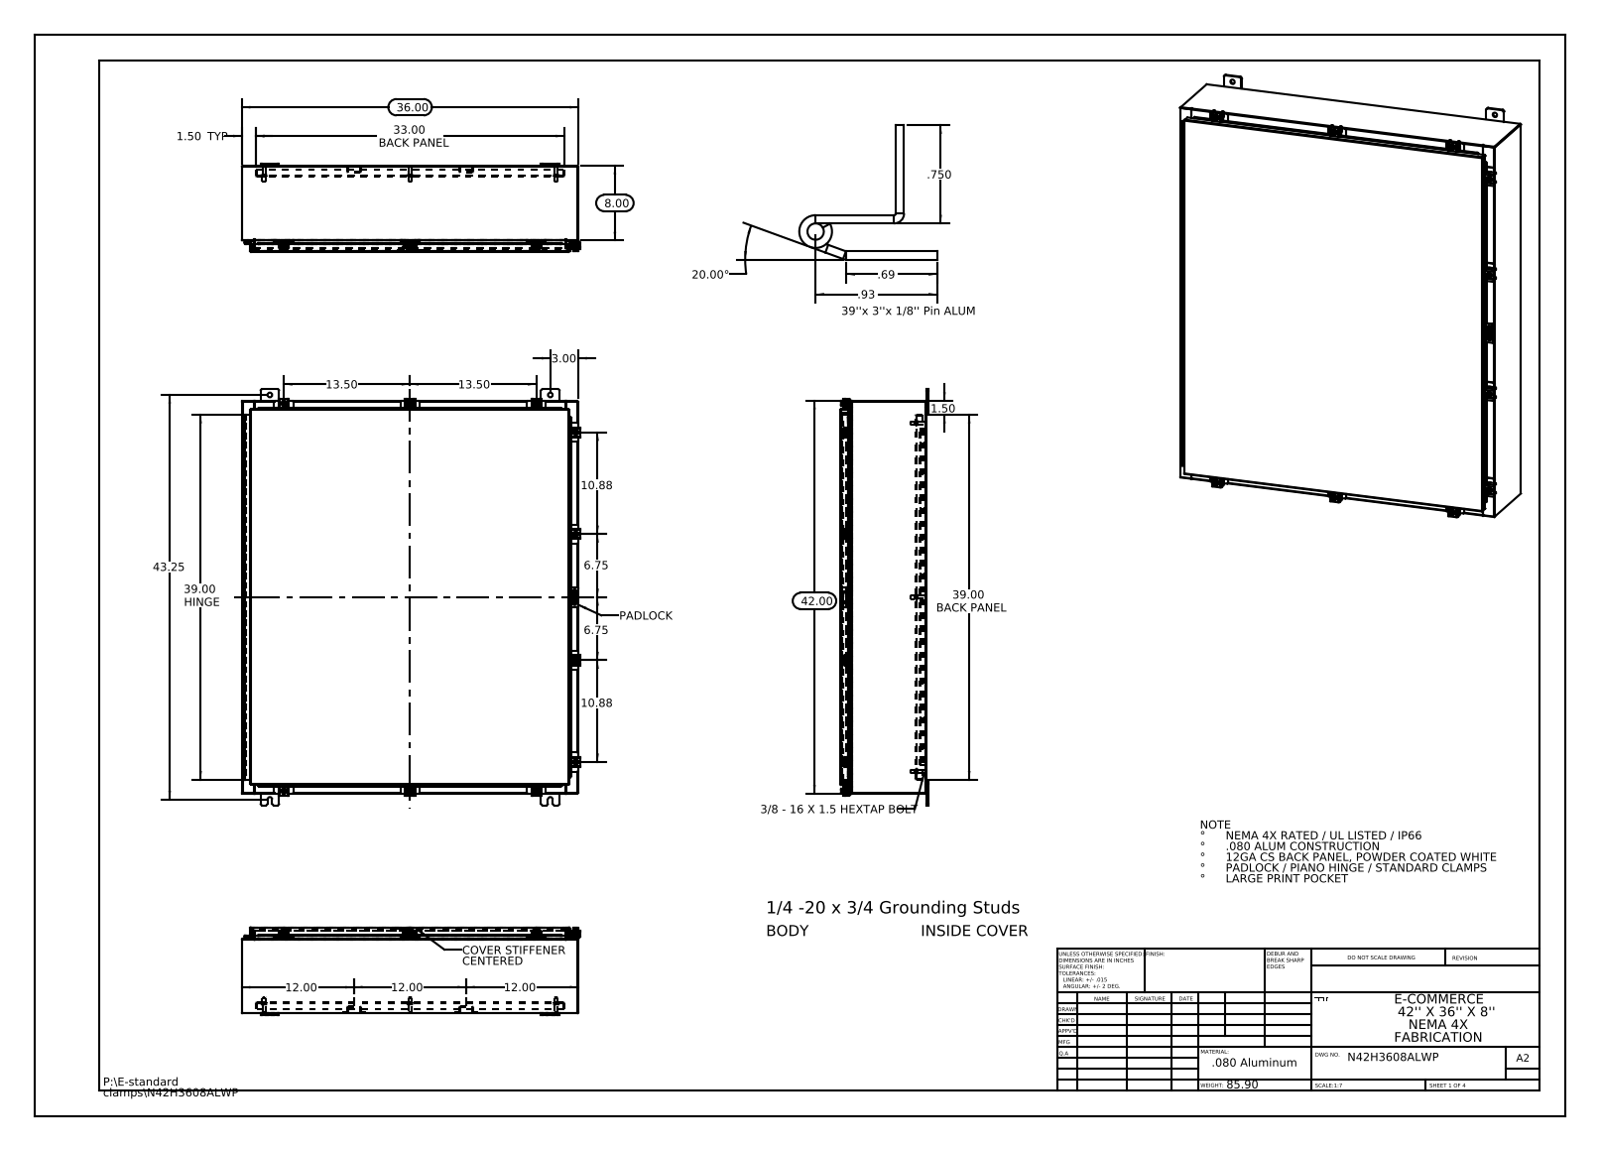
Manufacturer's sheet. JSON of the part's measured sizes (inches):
{"part_name": "N42H3608ALWP Clamp Assembly; N42H3608ALWP Clamp Bracket; N42H3608ALWP 22101002; N42H3608ALWP Padlock Hasp (+8 more)", "step_written_by": "SolidWorks 2013 (CONFIG_CONTROL_DESIGN)", "units": "inches", "bodies": {"solids": 74, "faces": 2855, "planar": 1490, "cylindrical": 1197, "other": 168}, "overall_size": [44.5, 36.211, 9.389], "volume_in3": 532, "surface_area_in2": 13223, "round_holes": [[0.5, 12], [0.213, 10], [0.26, 10], [0.25, 6], [0.125, 2], [0.125, 1]], "round_bosses_or_shafts": [[0.25, 11], [0.5, 10], [0.399, 10], [0.625, 8], [0.375, 8], [0.33, 8]], "partial_cylinders_radius": [[0.06, 46], [0.013, 39], [0.088, 33], [0.19, 24], [0.12, 20], [0.141, 20], [0.05, 15], [0.08, 14]], "face_to_face_distances": [0.075, 9.126, 9.051, 9.201, 0.104, 1, 8.126, 1.075, 8.051, 1.179], "hole_center_spacings": [13.5, 13.663, 17, 17.145, 18.625, 20.834, 24.311, 25.956]}
